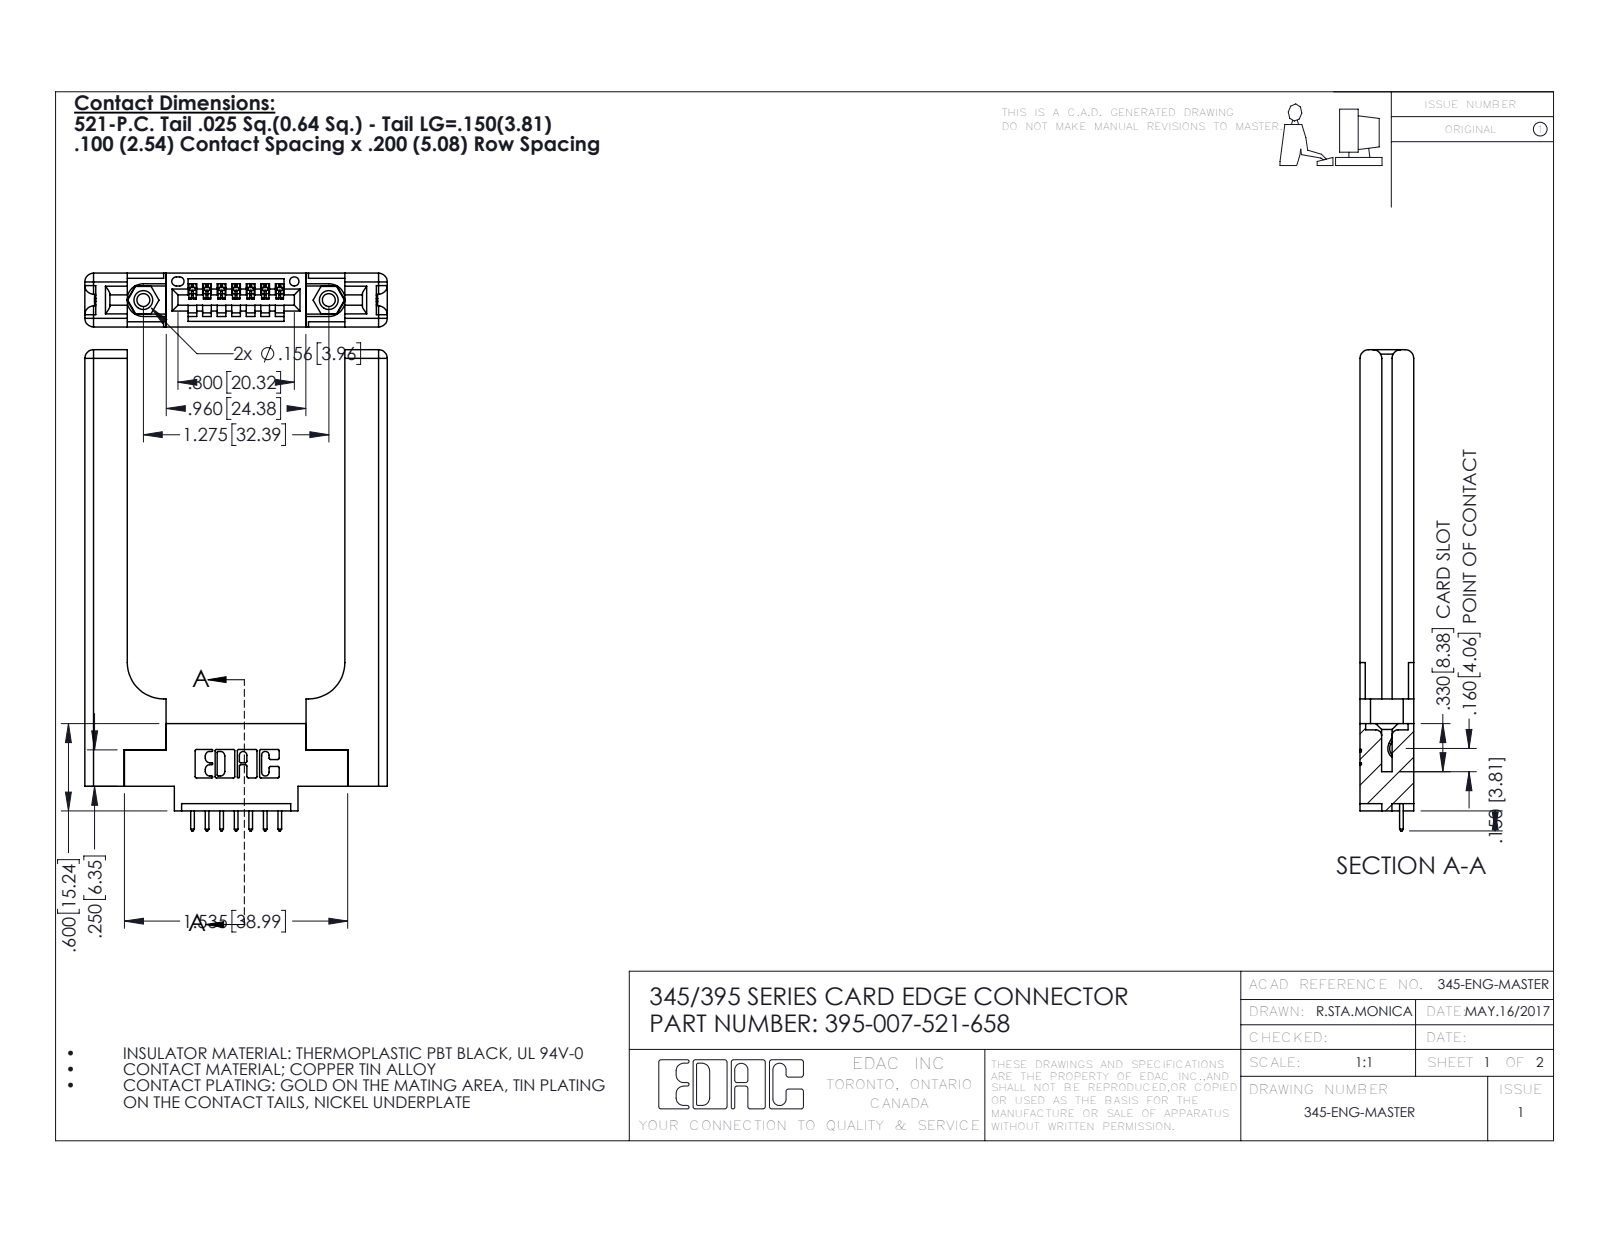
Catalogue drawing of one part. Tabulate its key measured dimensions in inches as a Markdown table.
| quantity | value |
| --- | --- |
| part name | 345-250-001_345-250-001-102; 345 Part_0.170 Offset - 0.156 Dia-TH; 345-292-001_345-293-121; 345-220-058_345-220-058 (+1 more) |
| STEP written by | SolidWorks 2016 (CONFIG_CONTROL_DESIGN) |
| units | inches |
| bodies | 12 solids, 792 faces (512 planar, 220 cylindrical, 60 other) |
| overall size | 3.307 × 2.079 × 0.37 |
| volume | 0.799 in³ |
| surface area | 17.03 in² |
| round holes (diameter × count) | 0.089 × 2, 0.125 × 2, 0.156 × 2, 0.064 × 1 |
| round bosses / shafts (diameter × count) | 0.155 × 2 |
| partial cylindrical surfaces (radius × count) | 0.01 × 22, 0.06 × 16, 0.006 × 14, 0.01 × 14, 0.007 × 6, 0.031 × 6, 0.026 × 3, 0.03 × 2 |
| main face-to-face distances | 0.37, 0.15, 0.22, 0.072, 0.148, 0.077, 1.496, 0.298, 0.071, 0.12 |
| hole center spacings | 0.27, 1.045, 1.275 |
